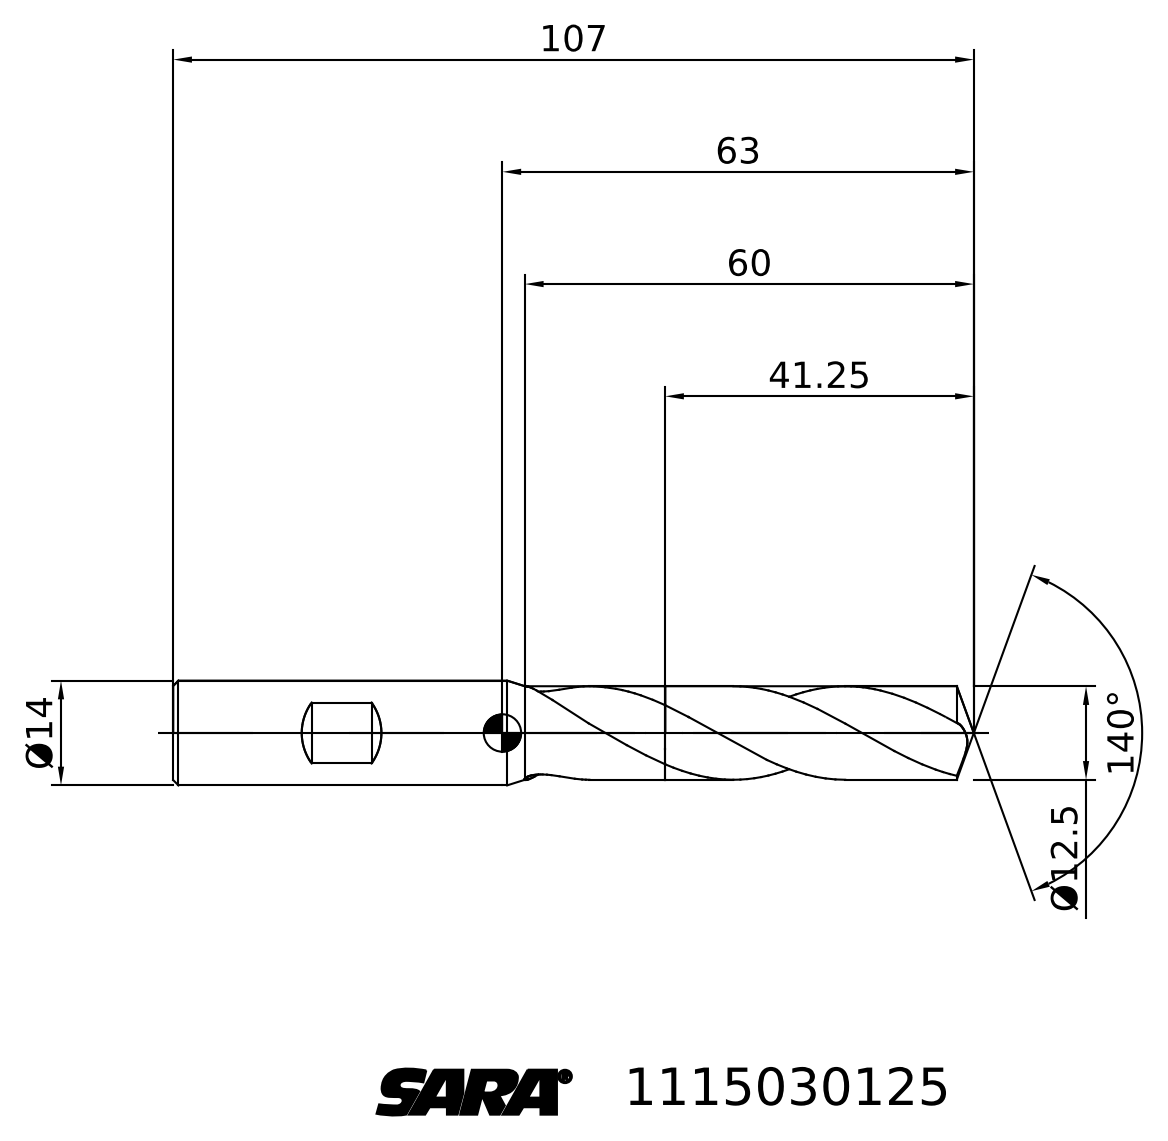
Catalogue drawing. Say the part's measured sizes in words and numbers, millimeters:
Its 3-D file was written by "TDM (AUTOMOTIVE_DESIGN)". It is 2 solids with 30 faces: 6 planar, 0 cylindrical and 24 other. Overall it measures 107 by 23.32 by 14 millimeters. Its volume is 12 000 cubic millimeters and its surface area 4 932 square millimeters. The main face-to-face distances are 65.75.
